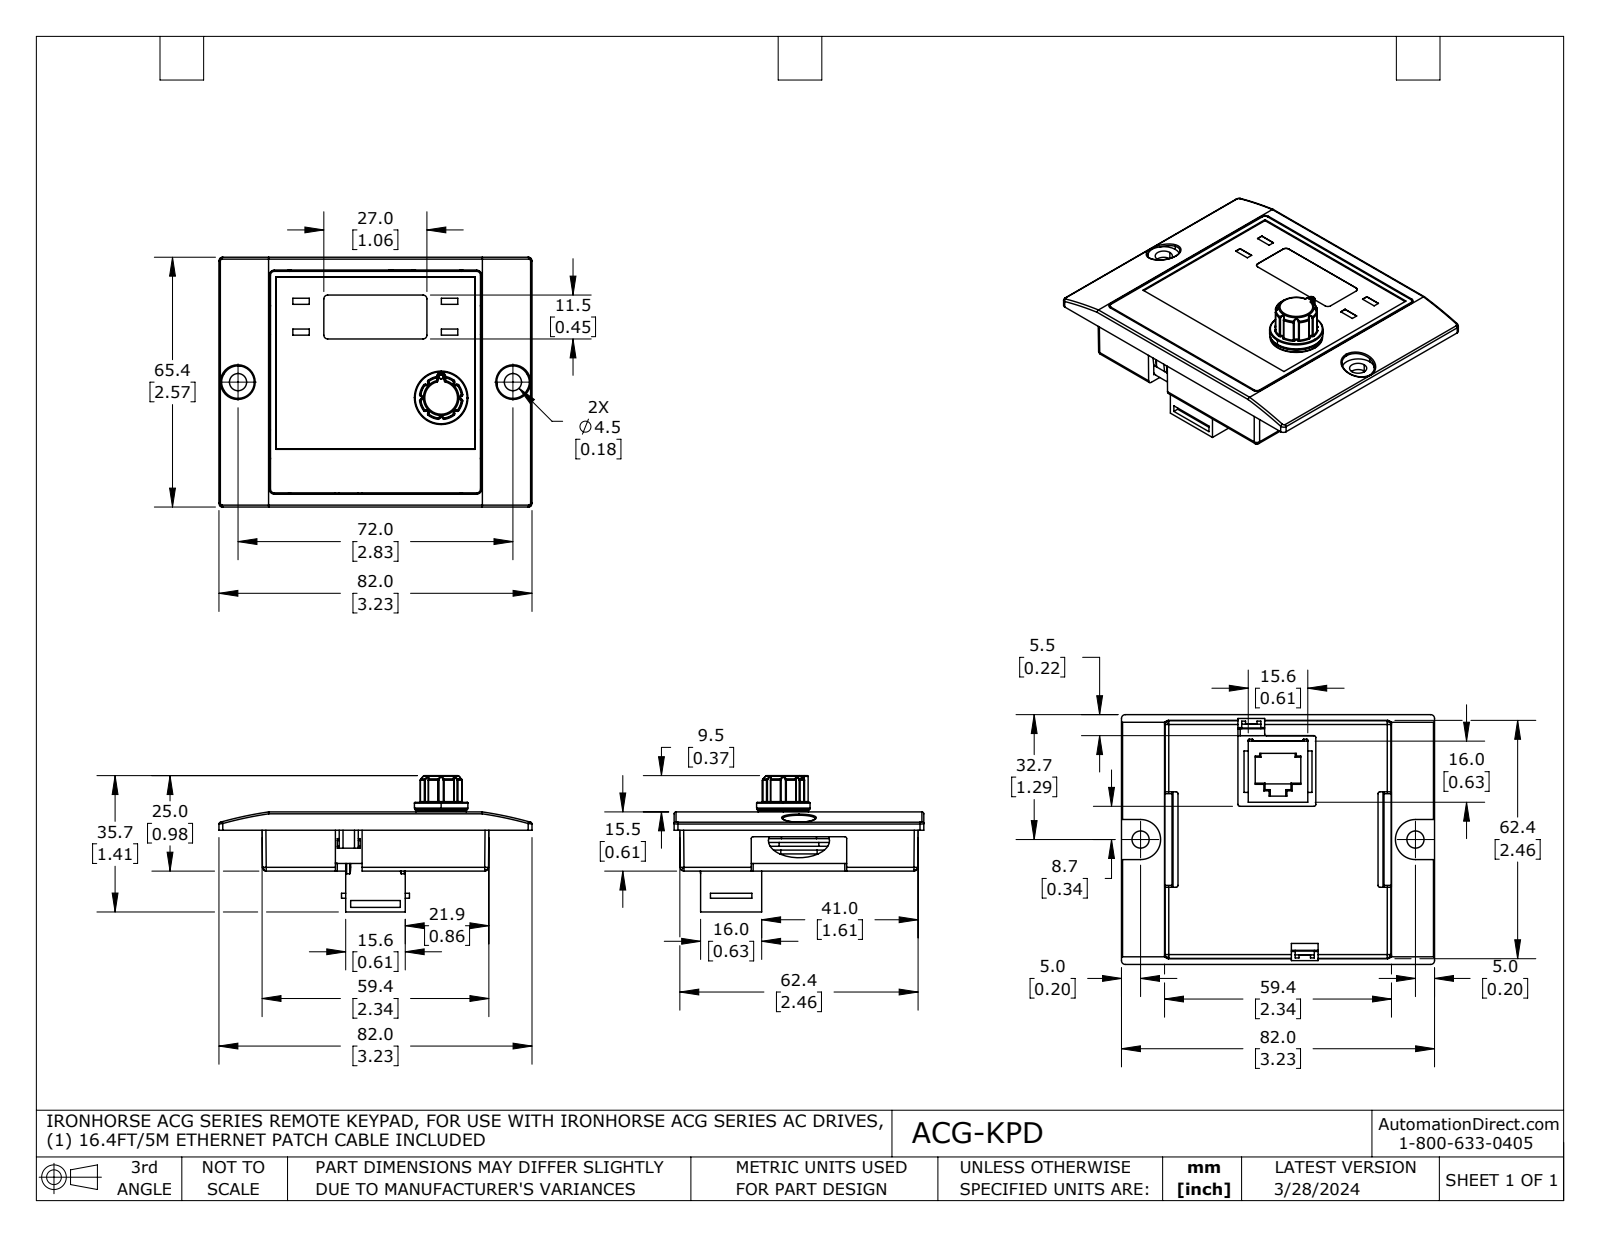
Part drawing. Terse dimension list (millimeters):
name: ACG-KPD
written by: SolidWorks 2021 (AUTOMOTIVE_DESIGN)
unit: mm
bodies: 8 solids, 2069 faces (783 planar, 556 cylindrical, 730 other)
size: 82 × 65.4 × 35.7
volume: 32 280 mm³; area: 39 320 mm²
holes: 6× ⌀3, 6× ⌀7.1, 2× ⌀4.5, 2× ⌀8.5, 1× ⌀1, 1× ⌀1.1, 1× ⌀5.2, 1× ⌀7
bosses: 2× ⌀1.7, 2× ⌀1.6, 2× ⌀1.3, 1× ⌀14, 1× ⌀13.8, 1× ⌀6.9, 1× ⌀6.8, 1× ⌀6.1
rounds: 172× R0.2, 42× R0.5, 36× R1, 20× R0.3, 12× R1.2, 12× R10, 9× R0.6, 8× R0.3
face distances: 13, 2, 15, 1.9, 2.3, 13.3, 15.3, 13.5, 0.5, 11
hole spacings: 12, 17.2, 12.3, 24, 27, 5.5, 13.1, 14.5
